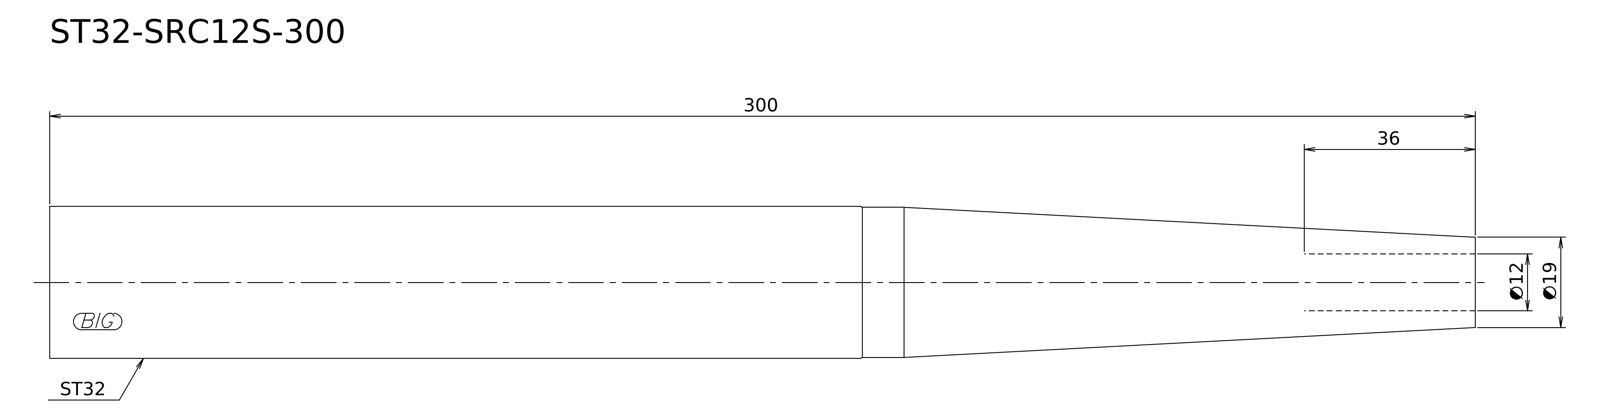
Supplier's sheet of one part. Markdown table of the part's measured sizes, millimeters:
| quantity | value |
| --- | --- |
| STEP written by | Kubotek KeyCreator V8.5.1 (14335) (CONFIG_CONTROL_DESIGN) |
| units | millimeters |
| bodies | 1 solid, 6 faces (2 planar, 2 cylindrical, 2 other) |
| overall size | 300 × 32 × 32 |
| volume | 206 098 mm³ |
| surface area | 28 724 mm² |
| round bosses / shafts (diameter × count) | 32 × 1, 31.6 × 1 |
| main face-to-face distances | 300 |
